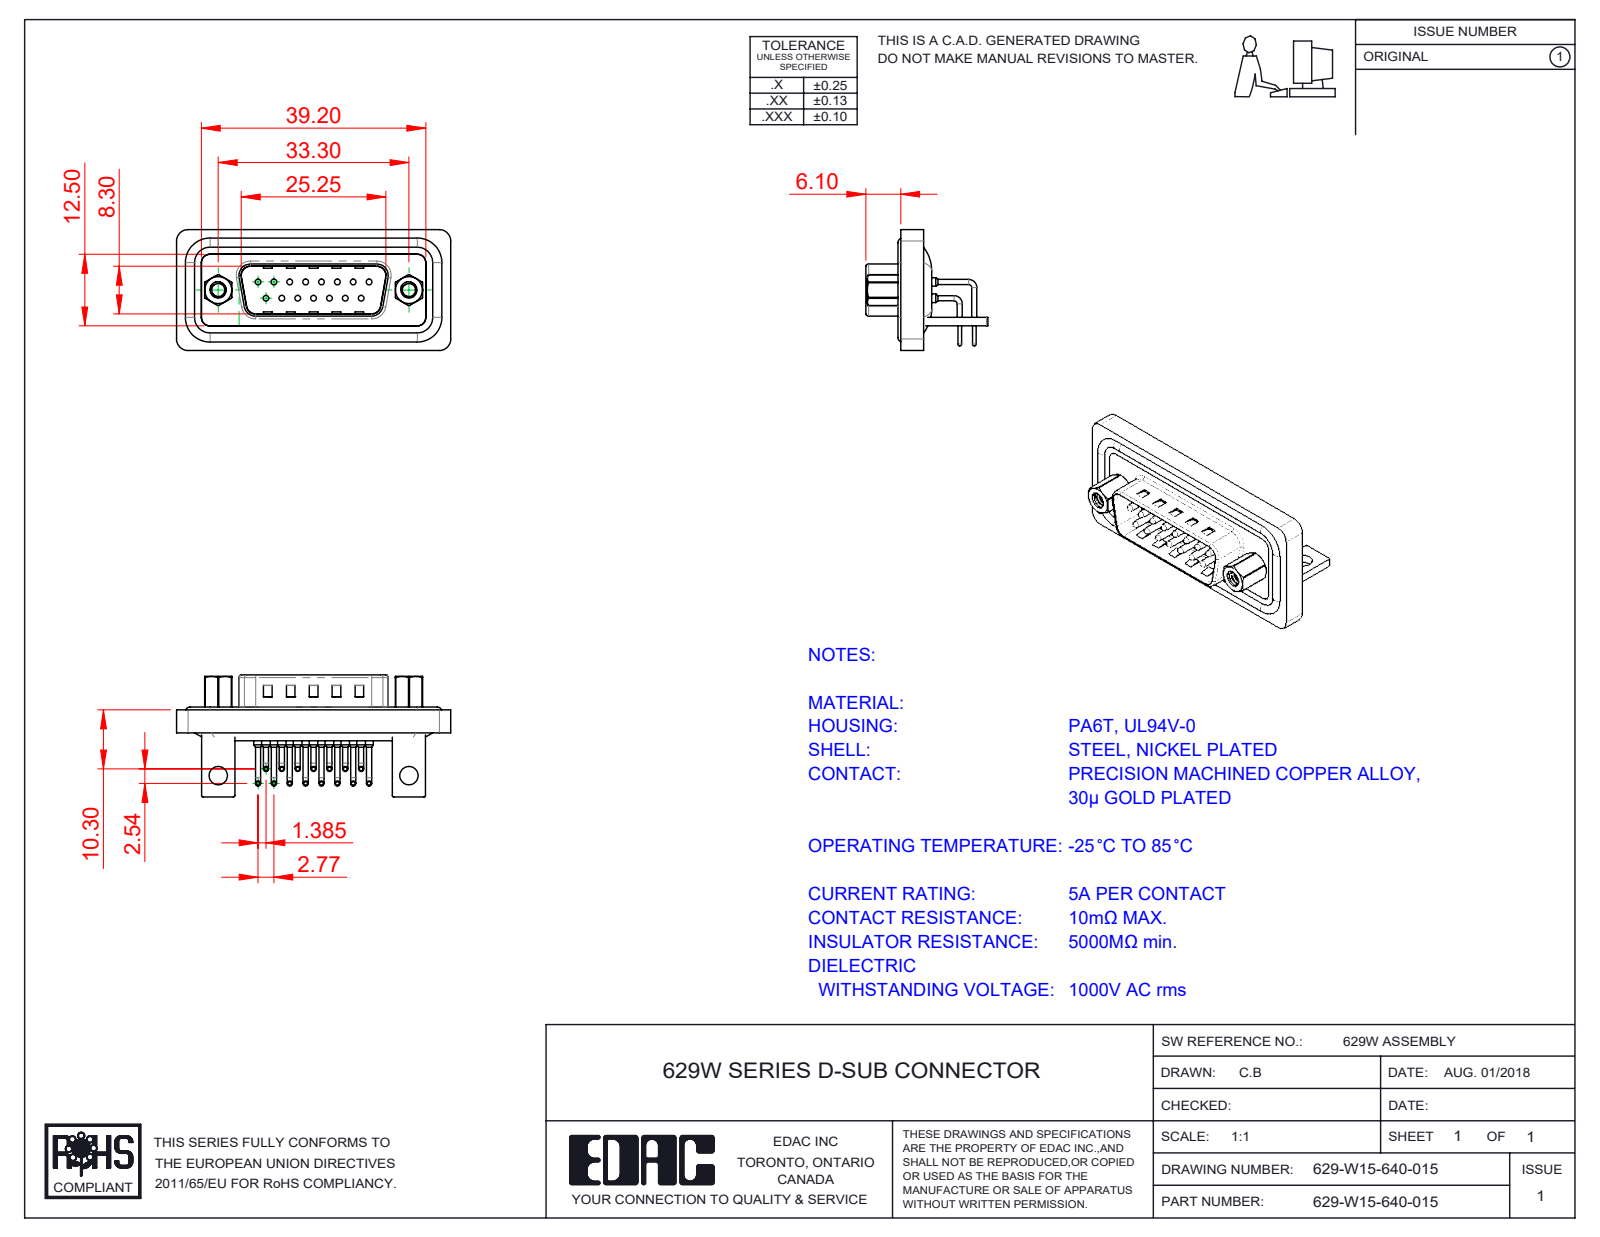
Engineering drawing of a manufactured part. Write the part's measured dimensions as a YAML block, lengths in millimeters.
part_name: "629W Shell_15 Contacts; 629W 4-40 Hex Standoff; 629W Waterproof Housing_15 Contacts; 629W Housing_15 Contacts (+5 more)"
step_written_by: "SolidWorks 2023 (CONFIG_CONTROL_DESIGN)"
units: millimeters
bodies: {solids: 25, faces: 2212, planar: 1155, cylindrical: 810, other: 247}
overall_size: [47.89, 21.5, 21.1]
volume: 5229
surface_area: 9122
round_holes:
  - {diameter: 1, count: 15}
  - {diameter: 1.5, count: 15}
  - {diameter: 1.7, count: 15}
  - {diameter: 2, count: 15}
  - {diameter: 2.26, count: 2}
  - {diameter: 2.29, count: 2}
  - {diameter: 3.2, count: 2}
  - {diameter: 4, count: 2}
  - {diameter: 4.8, count: 2}
  - {diameter: 4.9, count: 2}
  - {diameter: 5, count: 2}
round_bosses_or_shafts:
  - {diameter: 0.9, count: 30}
  - {diameter: 1.5, count: 15}
  - {diameter: 0.65, count: 15}
  - {diameter: 1.6, count: 4}
  - {diameter: 2.79, count: 2}
  - {diameter: 5, count: 1}
partial_cylinders:
  - {radius: 2, count: 17}
  - {radius: 1.01, count: 15}
  - {radius: 1.5, count: 14}
  - {radius: 0.25, count: 12}
  - {radius: 0.5, count: 9}
  - {radius: 2.7, count: 6}
  - {radius: 0.9, count: 4}
  - {radius: 1.6, count: 4}
face_to_face_distances: [0.4, 1.6, 1.1, 2.5, 2.9, 4.3, 1.5, 0.5, 4.5, 2.1]
hole_center_spacings: [3.16, 2.77, 5.54, 8.31, 3.17, 3.15, 11.08, 5.03]
